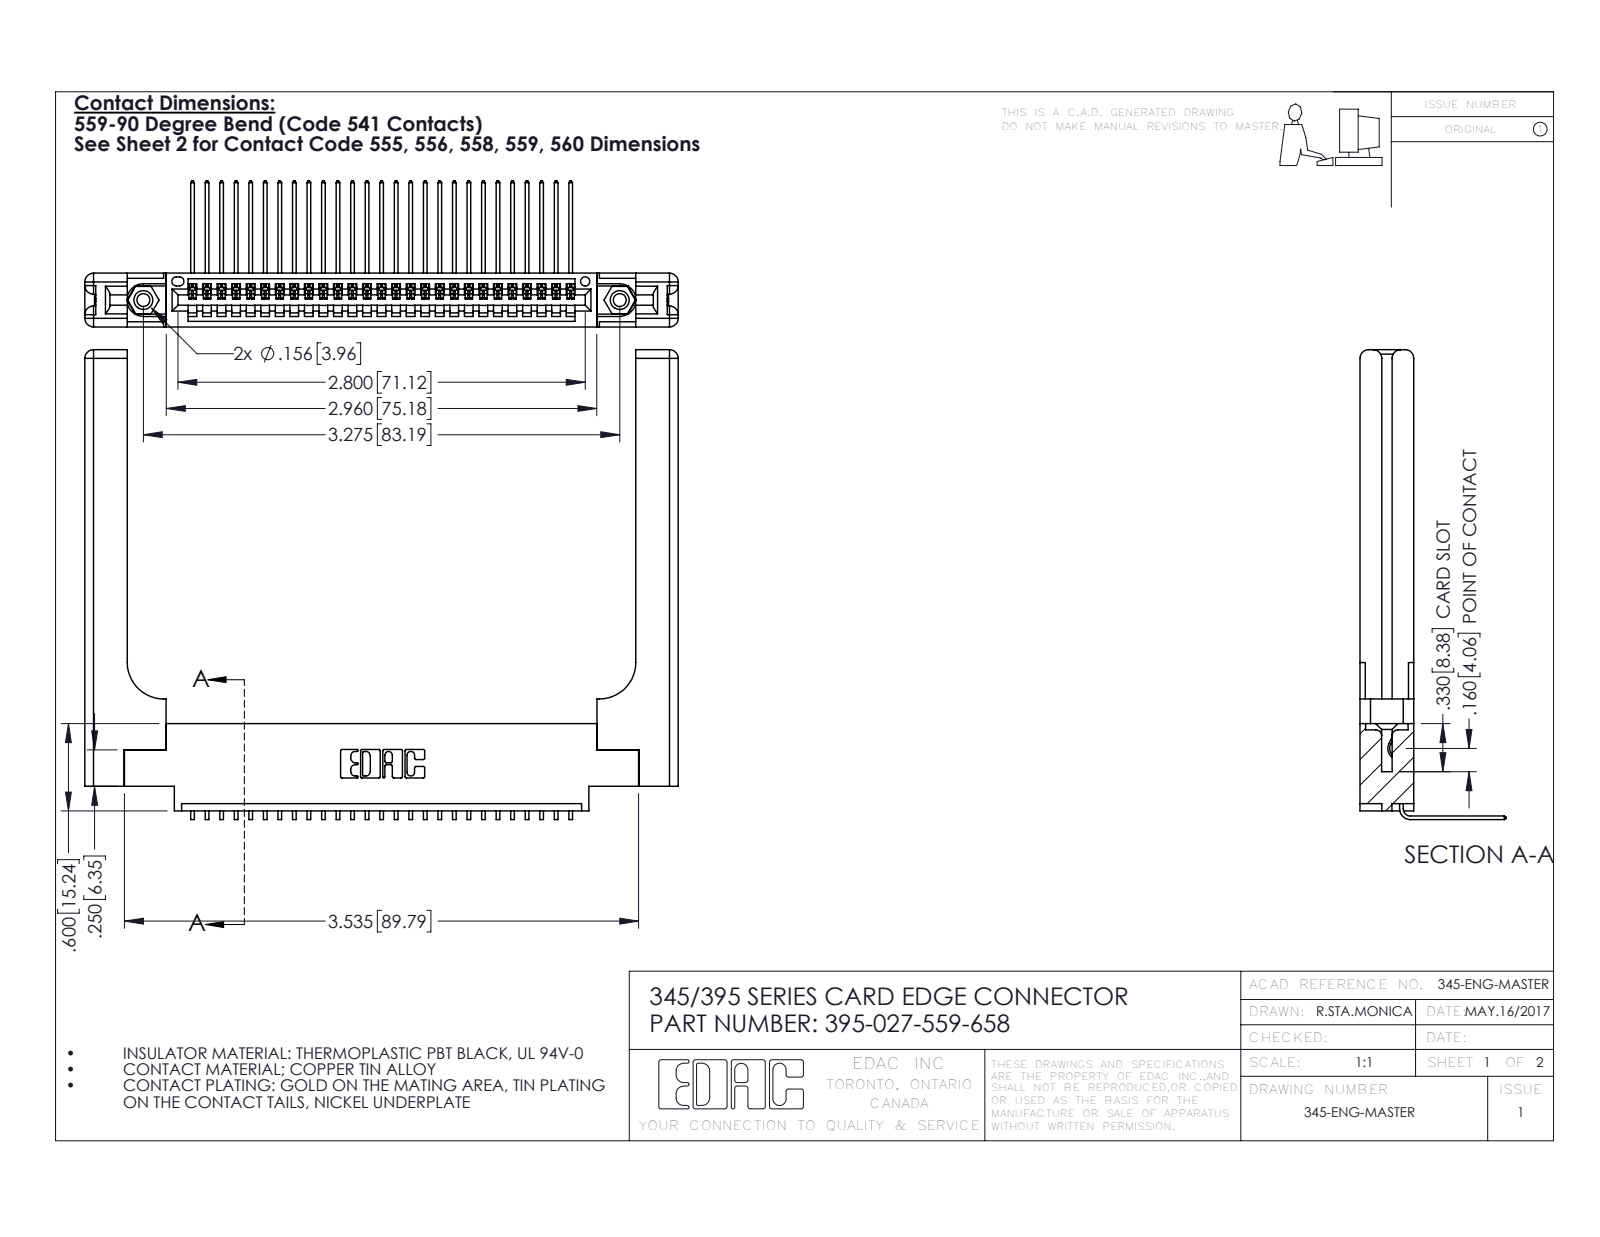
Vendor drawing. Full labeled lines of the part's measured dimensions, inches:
Part name (STEP PRODUCT): 395-027-559-658; 345 Part_0.170 Offset - 0.156 Dia-TH; 345-220-058_345-220-058; 345-250-001_345-250-001-102 (+1 more)
STEP written by: SolidWorks 2016 (CONFIG_CONTROL_DESIGN)
Units: inches
Bodies: 32 solids, 2006 faces (1366 planar, 580 cylindrical, 60 other)
Overall size (bounding box): 4.079 × 3.229 × 1.005
Volume: 1.111 in³ · Surface area: 28.89 in²
Round holes (diameter × count): ⌀0.089 ×2, ⌀0.125 ×2, ⌀0.156 ×2, ⌀0.064 ×1
Round bosses / shafts (diameter × count): ⌀0.155 ×2
Partial cylindrical surfaces — rounded edges, fillets, slot ends (radius × count): R0.006 ×54, R0.01 ×22, R0.06 ×16, R0.007 ×6, R0.031 ×6, R0.026 ×3, R0.03 ×2, R0.031 ×2
Main face-to-face distances: 0.37, 0.072, 0.298, 0.148, 0.15, 0.077, 0.098, 0.272, 0.025, 0.2
Hole centre spacings: 0.27, 3.04, 3.275
